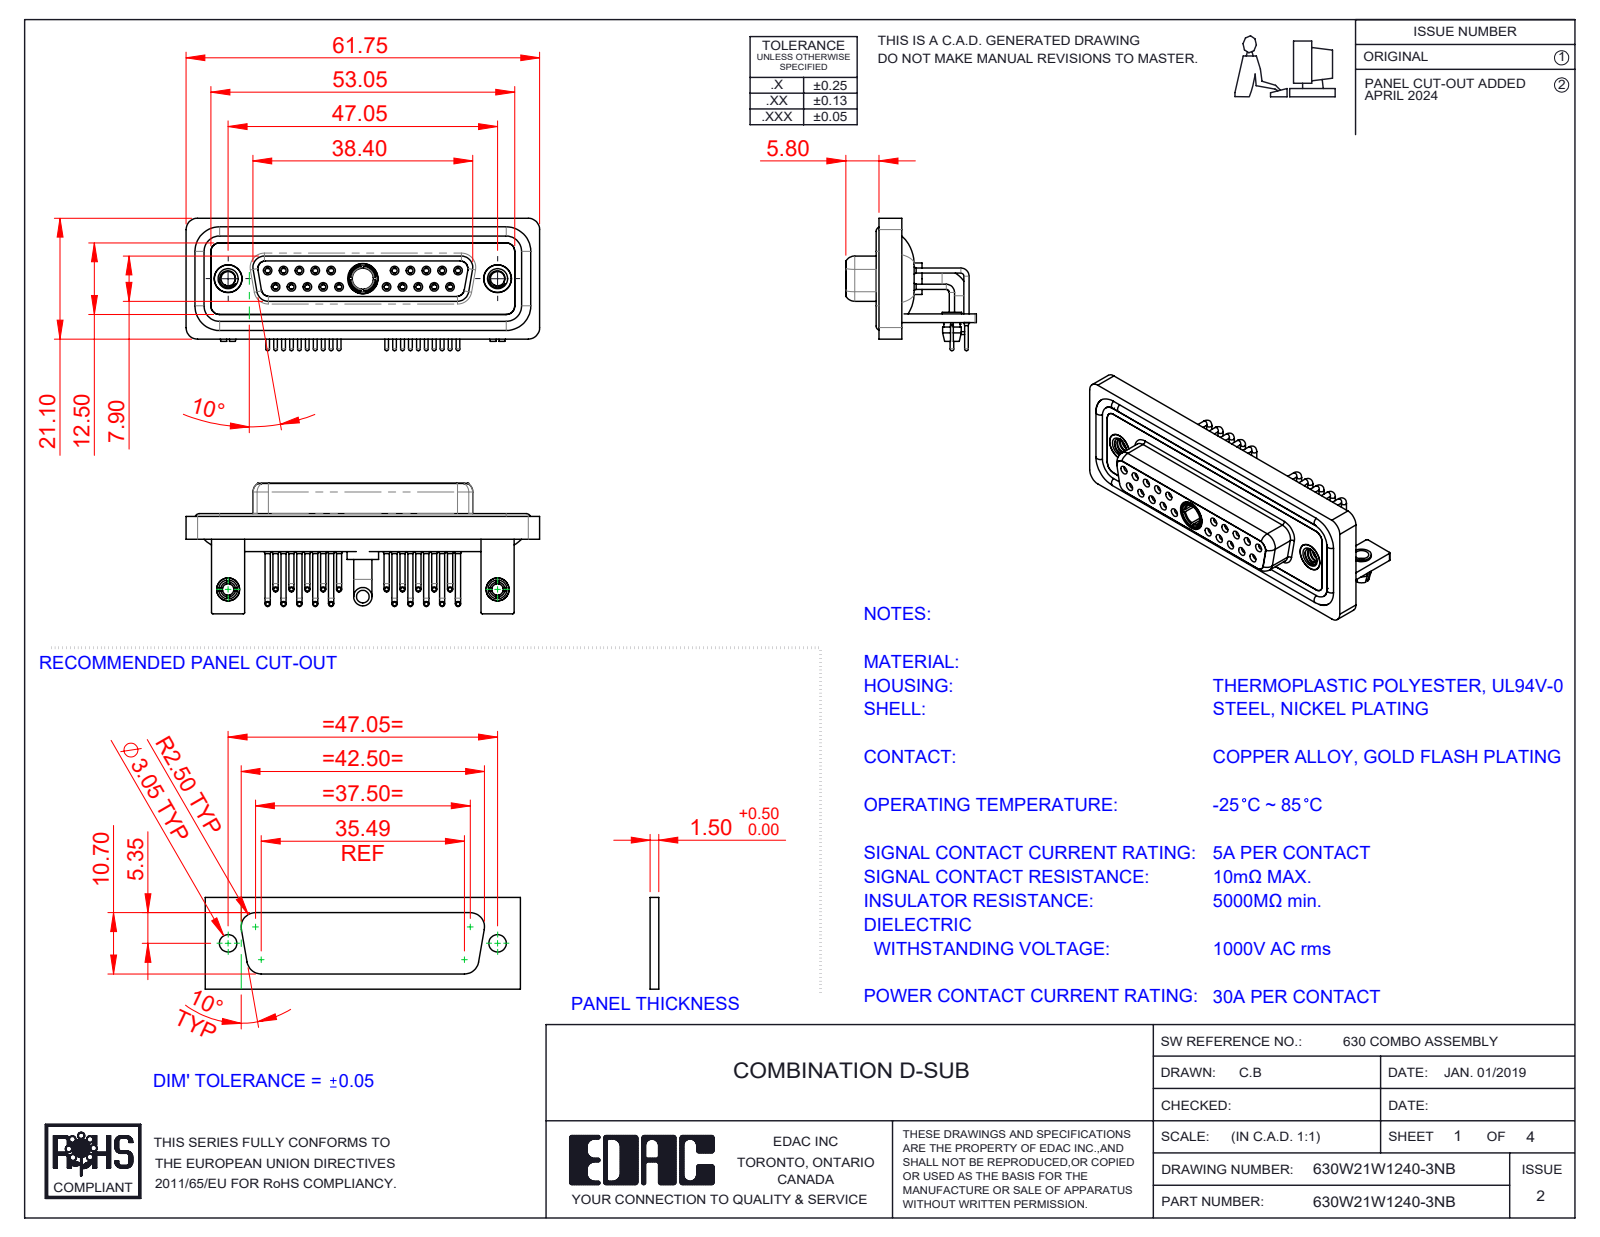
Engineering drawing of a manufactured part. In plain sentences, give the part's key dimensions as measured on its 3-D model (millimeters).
The part is named "630Combo Housing_21W1; 630Combo Shell Rear_25 Contacts; Power Socket_30A RA; 630Combo Threaded Rivet_A (+7 more)". Its 3-D file was written by "SolidWorks 2023 (CONFIG_CONTROL_DESIGN)". It is 33 solids with 1658 faces: 502 planar, 727 cylindrical and 429 other. Overall it measures 61.75 by 23.12 by 22.8 millimeters. Its volume is 8 929 cubic millimeters and its surface area 15 747 square millimeters. Round holes: 22 of diameter 2, 20 of diameter 0.9, 20 of diameter 1.1, 20 of diameter 1.5, 10 of diameter 1.6, 10 of diameter 1.7, 4 of diameter 2.5, 3 of diameter 4.85, 2 of diameter 3.2, 2 of diameter 4, 2 of diameter 4.05, 2 of diameter 5. Round bosses or shafts: 20 of diameter 0.9, 20 of diameter 0.65, 14 of diameter 1.6, 2 of diameter 4.95, 2 of diameter 4.8, 2 of diameter 4, 2 of diameter 3.4, 2 of diameter 3.3. Partial cylindrical surfaces (rounded edges, fillets, slot ends): 19 of radius 2, 18 of radius 1.5, 16 of radius 0.25, 8 of radius 1.35, 8 of radius 1.6, 5 of radius 0.5, 4 of radius 0.6, 4 of radius 0.65. The main face-to-face distances are 0.4, 1.8, 2.9, 3.7, 1.5, 4.1, 1.1, 1.4, 1.6, 2.5. The hole center spacings are 3.16, 2.77, 5.54, 8.31, 5.04, 19.39, 20.97, 22.16.
